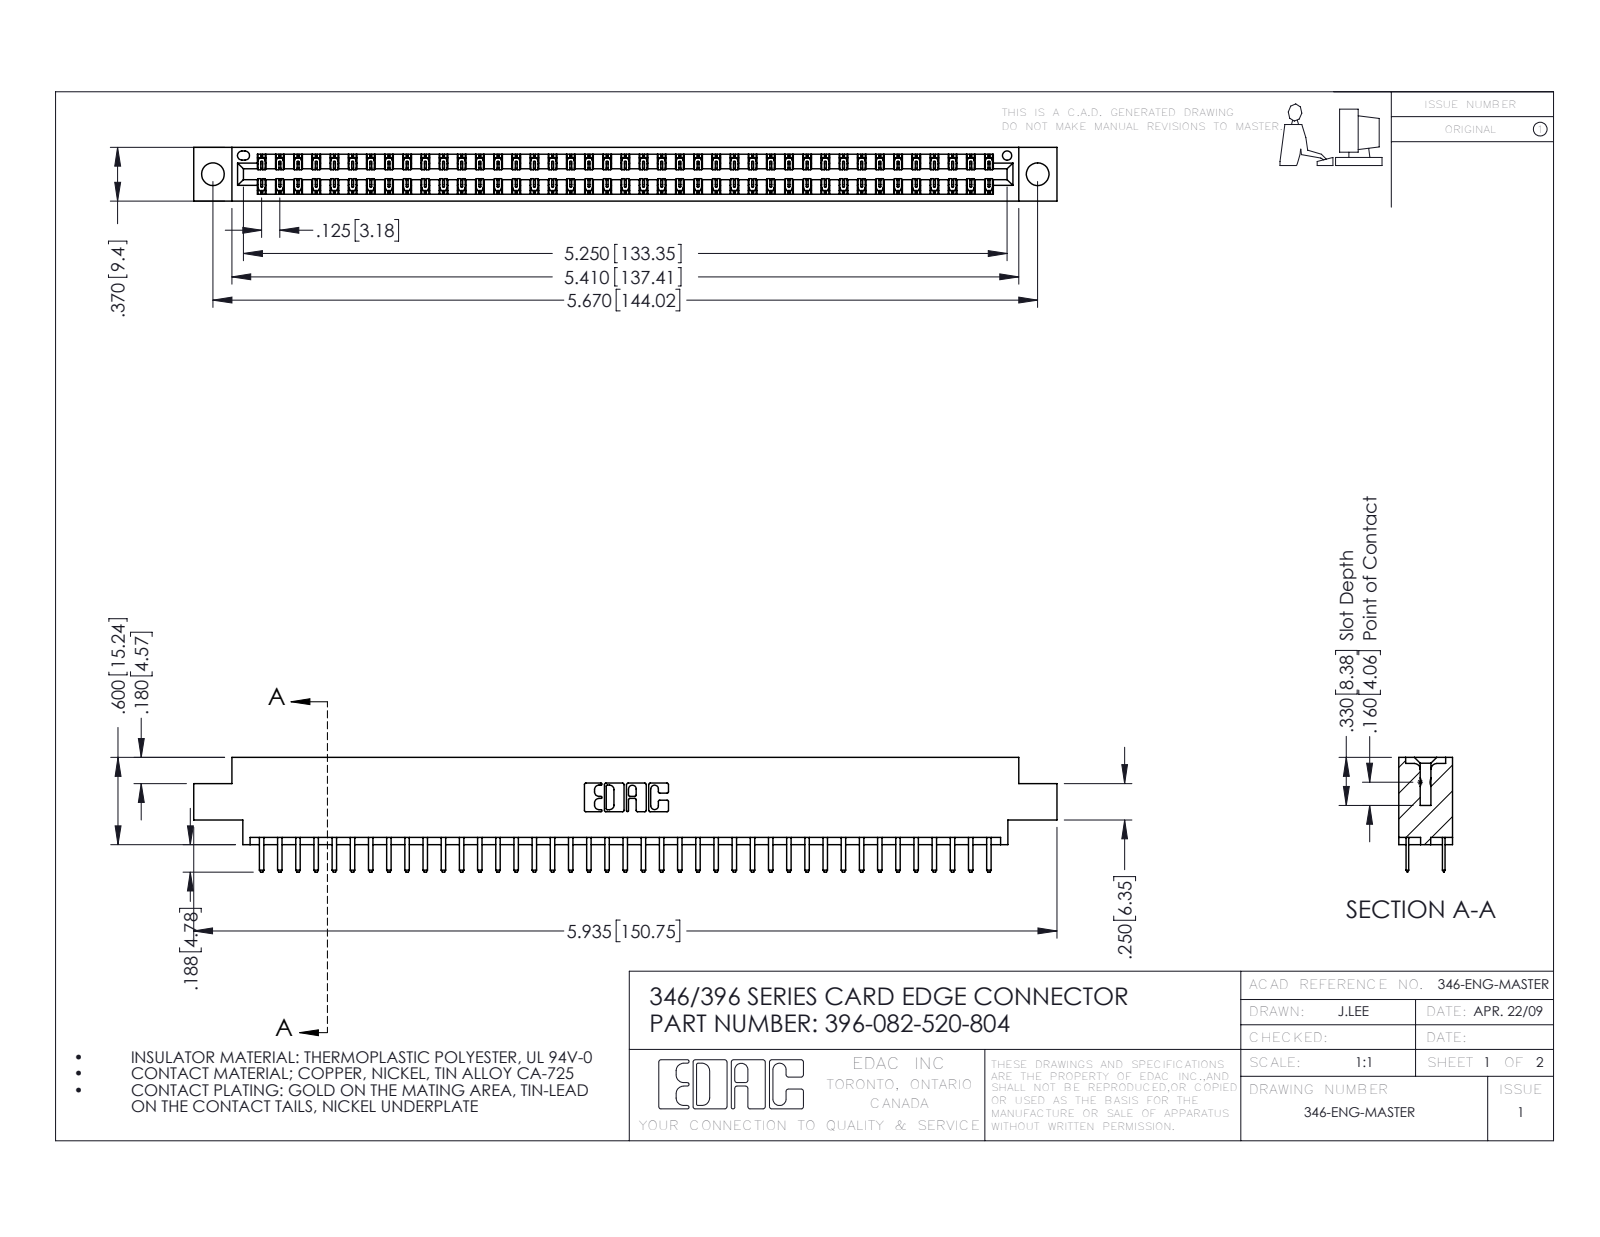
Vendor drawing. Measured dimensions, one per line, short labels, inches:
name: 396-082-520-804; 346 Part_0.170 Offset - 0.156 Dia-TH; 345-292-001_345-293-120
written by: SolidWorks 2016 (CONFIG_CONTROL_DESIGN)
unit: in
bodies: 83 solids, 4718 faces (3114 planar, 1604 cylindrical, 0 other)
size: 5.935 × 0.788 × 0.37
volume: 0.88 in³; area: 30.54 in²
holes: 2× ⌀0.156, 1× ⌀0.064
rounds: 123× R0.006, 86× R0.01, 22× R0.01, 6× R0.007, 6× R0.031, 3× R0.026, 2× R0.014, 2× R0.022
face distances: 0.048, 0.322, 0.37, 0.25, 0.275, 0.072, 0.298, 0.025, 0.148, 0.222
hole spacings: 0.246, 5.461, 5.67
